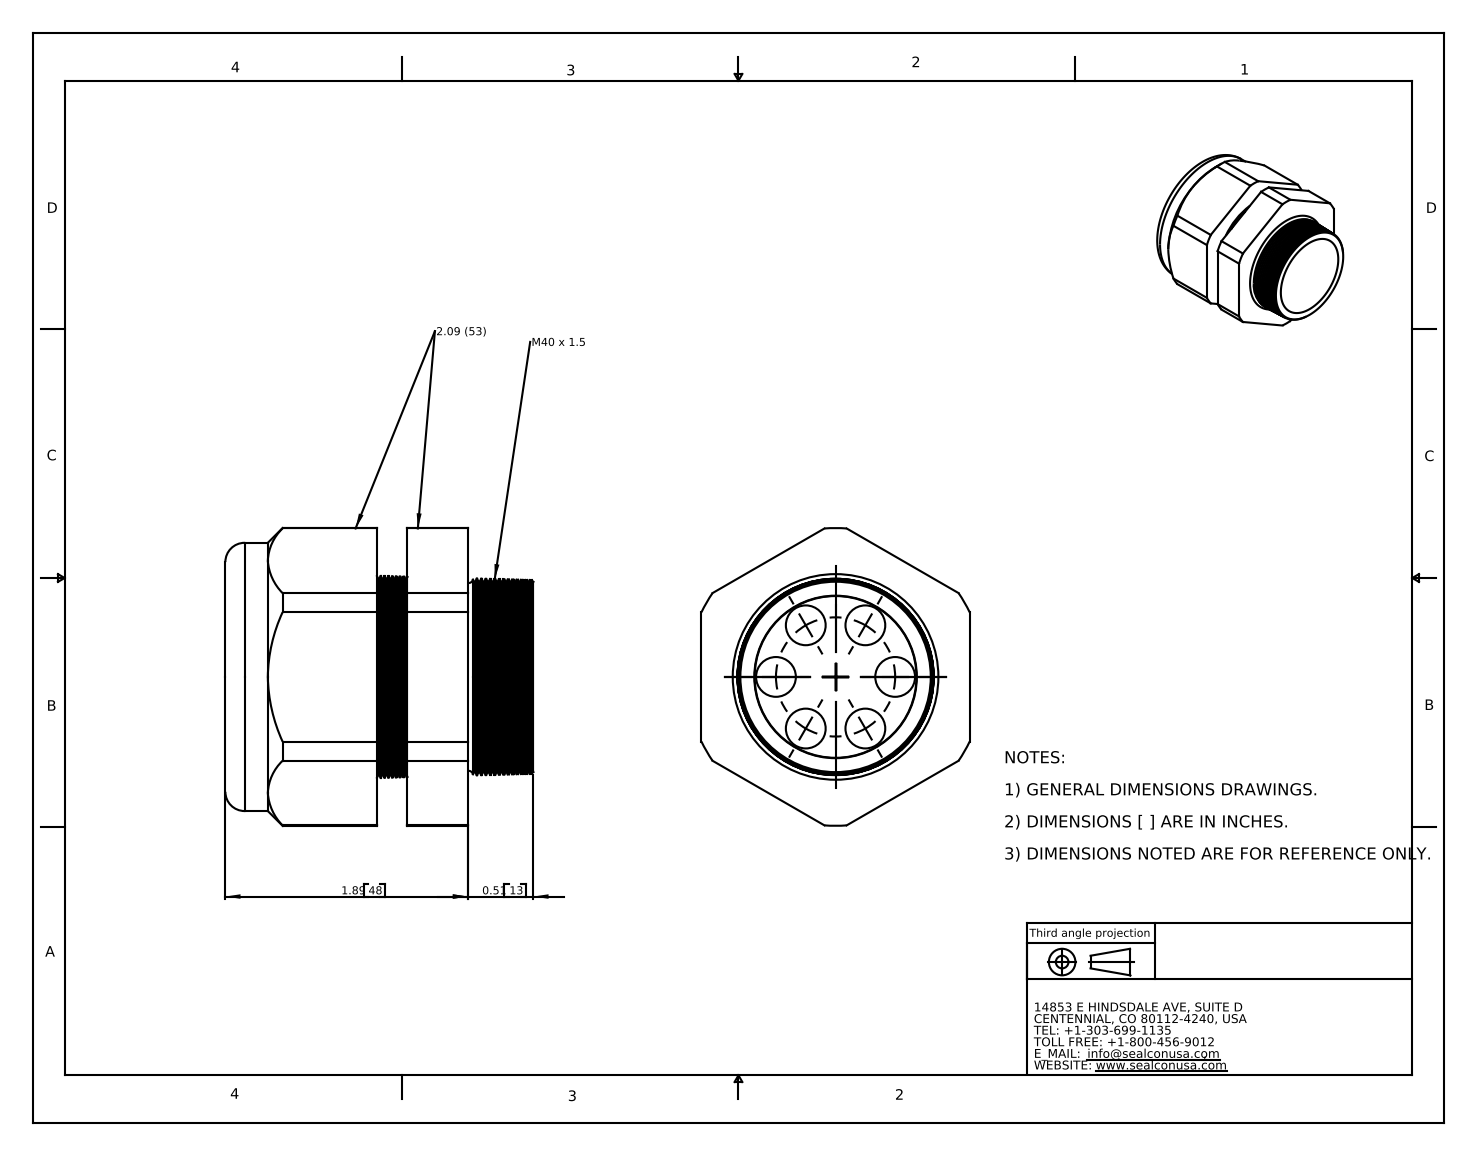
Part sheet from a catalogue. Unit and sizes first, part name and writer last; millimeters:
Units: millimetres
Overall size (bounding box): 61 × 58.9 × 53.1
Round holes (diameter × count): ⌀7.9 ×6, ⌀31.5 ×1, ⌀32 ×1
Round bosses / shafts (diameter × count): ⌀53.1 ×1
Partial cylindrical surfaces — rounded edges, fillets, slot ends (radius × count): R29.5 ×1
Main face-to-face distances: 53.1, 6, 18, 12, 30, 36, 48, 12.7, 17.3, 23.3
Hole centre spacings: 11.8, 11.8, 20.4, 20.4, 23.6, 23.6
Volume: 78 310 mm³ · Surface area: 27 140 mm²
Bodies: 2 solids, 201 faces (21 planar, 32 cylindrical, 148 other)
Part name (STEP PRODUCT): CD40M3-GY
STEP written by: SolidWorks 2007 (CONFIG_CONTROL_DESIGN)
